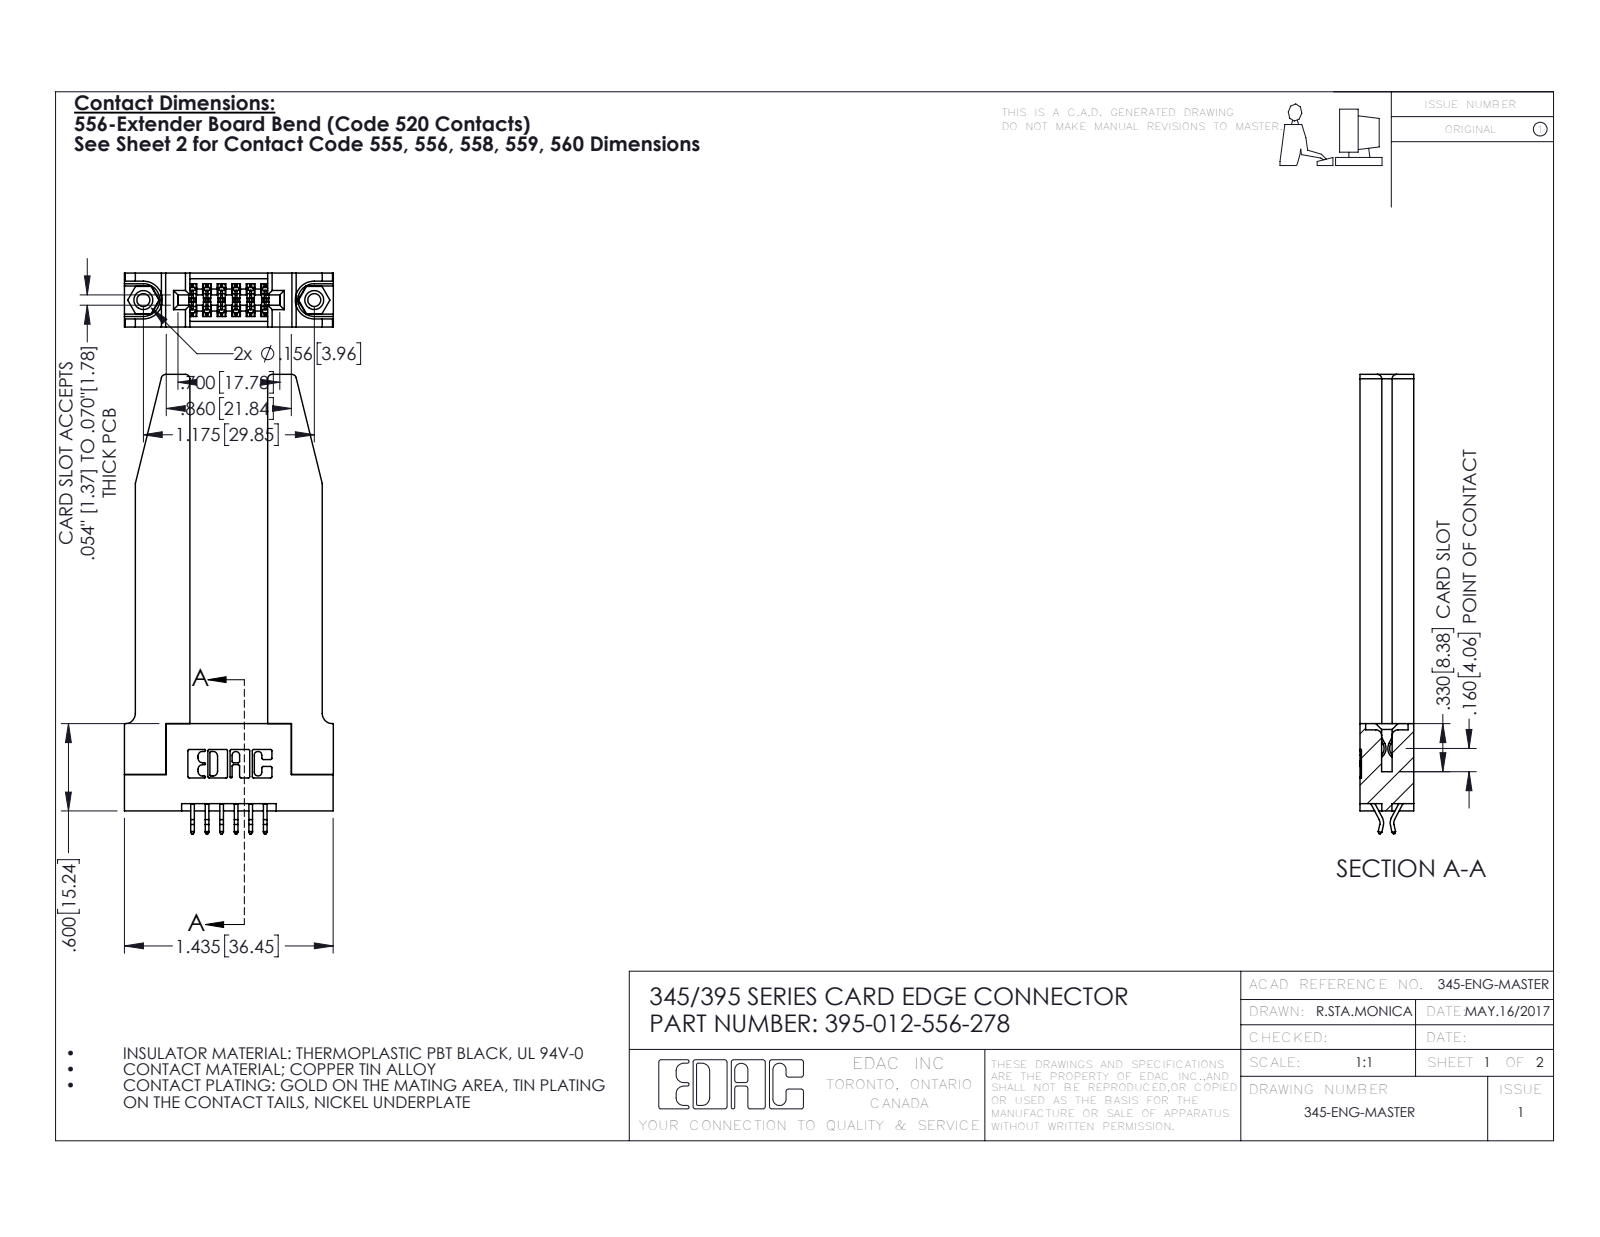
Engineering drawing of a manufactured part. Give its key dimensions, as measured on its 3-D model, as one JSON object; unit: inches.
{"part_name": "345 Part_Flush Mounting Lugs - 0.156 Dia-TH; 345-250-001_345-250-001-102; 395-012-556-278; 345-220-078_345-220-078 (+1 more)", "step_written_by": "SolidWorks 2016 (CONFIG_CONTROL_DESIGN)", "units": "inches", "bodies": {"solids": 17, "faces": 1032, "planar": 666, "cylindrical": 314, "other": 52}, "overall_size": [3.157, 1.436, 0.37], "volume_in3": 0.67, "surface_area_in2": 16.85, "round_holes": [[0.089, 2], [0.125, 2], [0.156, 2], [0.064, 1]], "round_bosses_or_shafts": [[0.155, 2]], "partial_cylinders_radius": [[0.01, 22], [0.006, 18], [0.03, 8], [0.007, 6], [0.031, 6], [0.026, 3], [0.01, 2], [0.014, 2]], "face_to_face_distances": [0.37, 0.15, 0.22, 0.535, 0.072, 0.148, 0.077, 0.298, 0.2, 0.095], "hole_center_spacings": [0.27, 0.946, 1.175]}
